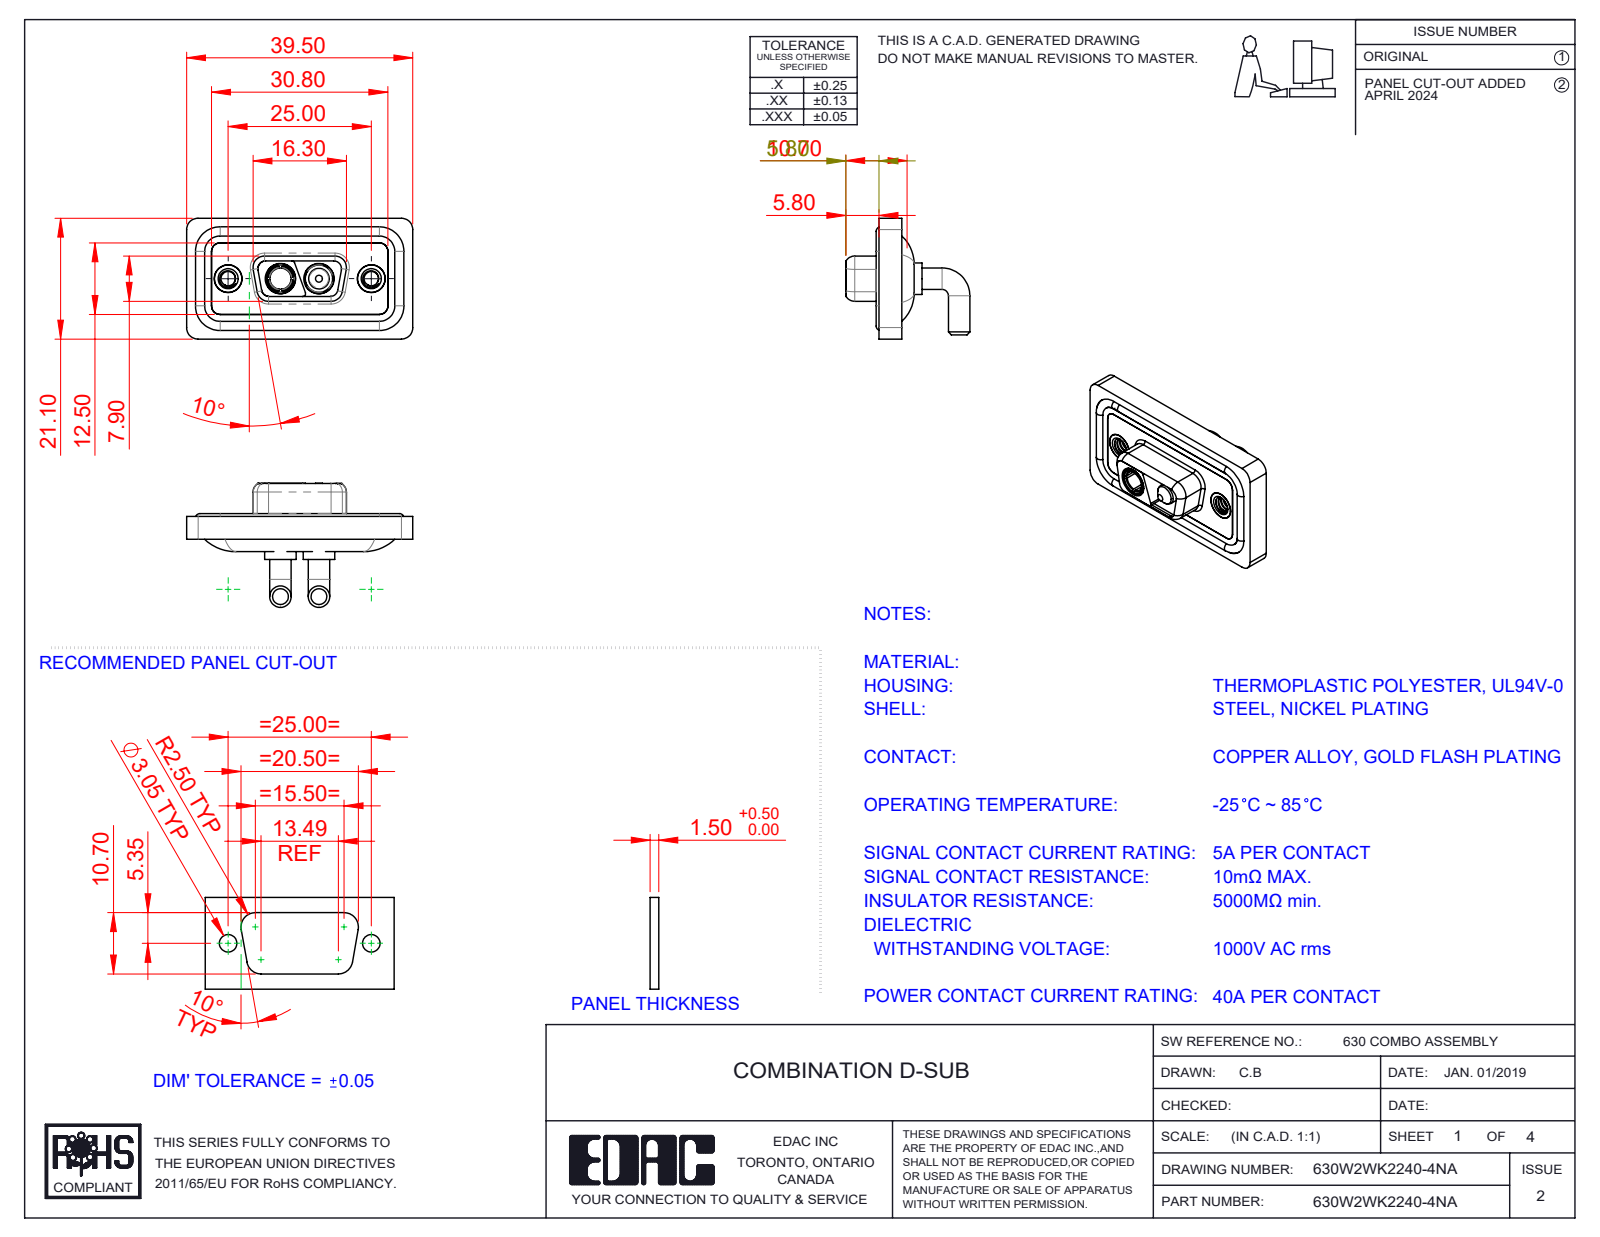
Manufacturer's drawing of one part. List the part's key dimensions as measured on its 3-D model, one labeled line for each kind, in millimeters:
Part name (STEP PRODUCT): 630Combo Waterproof Housing_09 Contacts; 630Combo Threaded Rivet_A; 630W2WK2140-4NA; Power Pin_40A RA (+4 more)
STEP written by: SolidWorks 2023 (CONFIG_CONTROL_DESIGN)
Units: millimetres
Bodies: 11 solids, 502 faces (144 planar, 233 cylindrical, 125 other)
Overall size (bounding box): 39.5 × 21.68 × 21.1
Volume: 4 845 mm³ · Surface area: 7 585 mm²
Round holes (diameter × count): ⌀4.85 ×4, ⌀2.5 ×2, ⌀4 ×2, ⌀4.05 ×2, ⌀5 ×2, ⌀5.3 ×2, ⌀3.7 ×1
Round bosses / shafts (diameter × count): ⌀3.75 ×4, ⌀1.6 ×4, ⌀5.5 ×2, ⌀5.2 ×2, ⌀4.95 ×2, ⌀4.8 ×2, ⌀4.75 ×2, ⌀4.96 ×1
Partial cylindrical surfaces — rounded edges, fillets, slot ends (radius × count): R1.5 ×18, R2 ×18, R1.35 ×8, R1.6 ×8, R0.5 ×6, R0.25 ×4, R0.6 ×4, R0.65 ×4
Main face-to-face distances: 0.4, 1.1, 2.9, 1.8, 2.5, 1.6, 3.1, 2.1, 3.7, 1.5
Hole centre spacings: 9.14, 15.86, 6.72, 25
